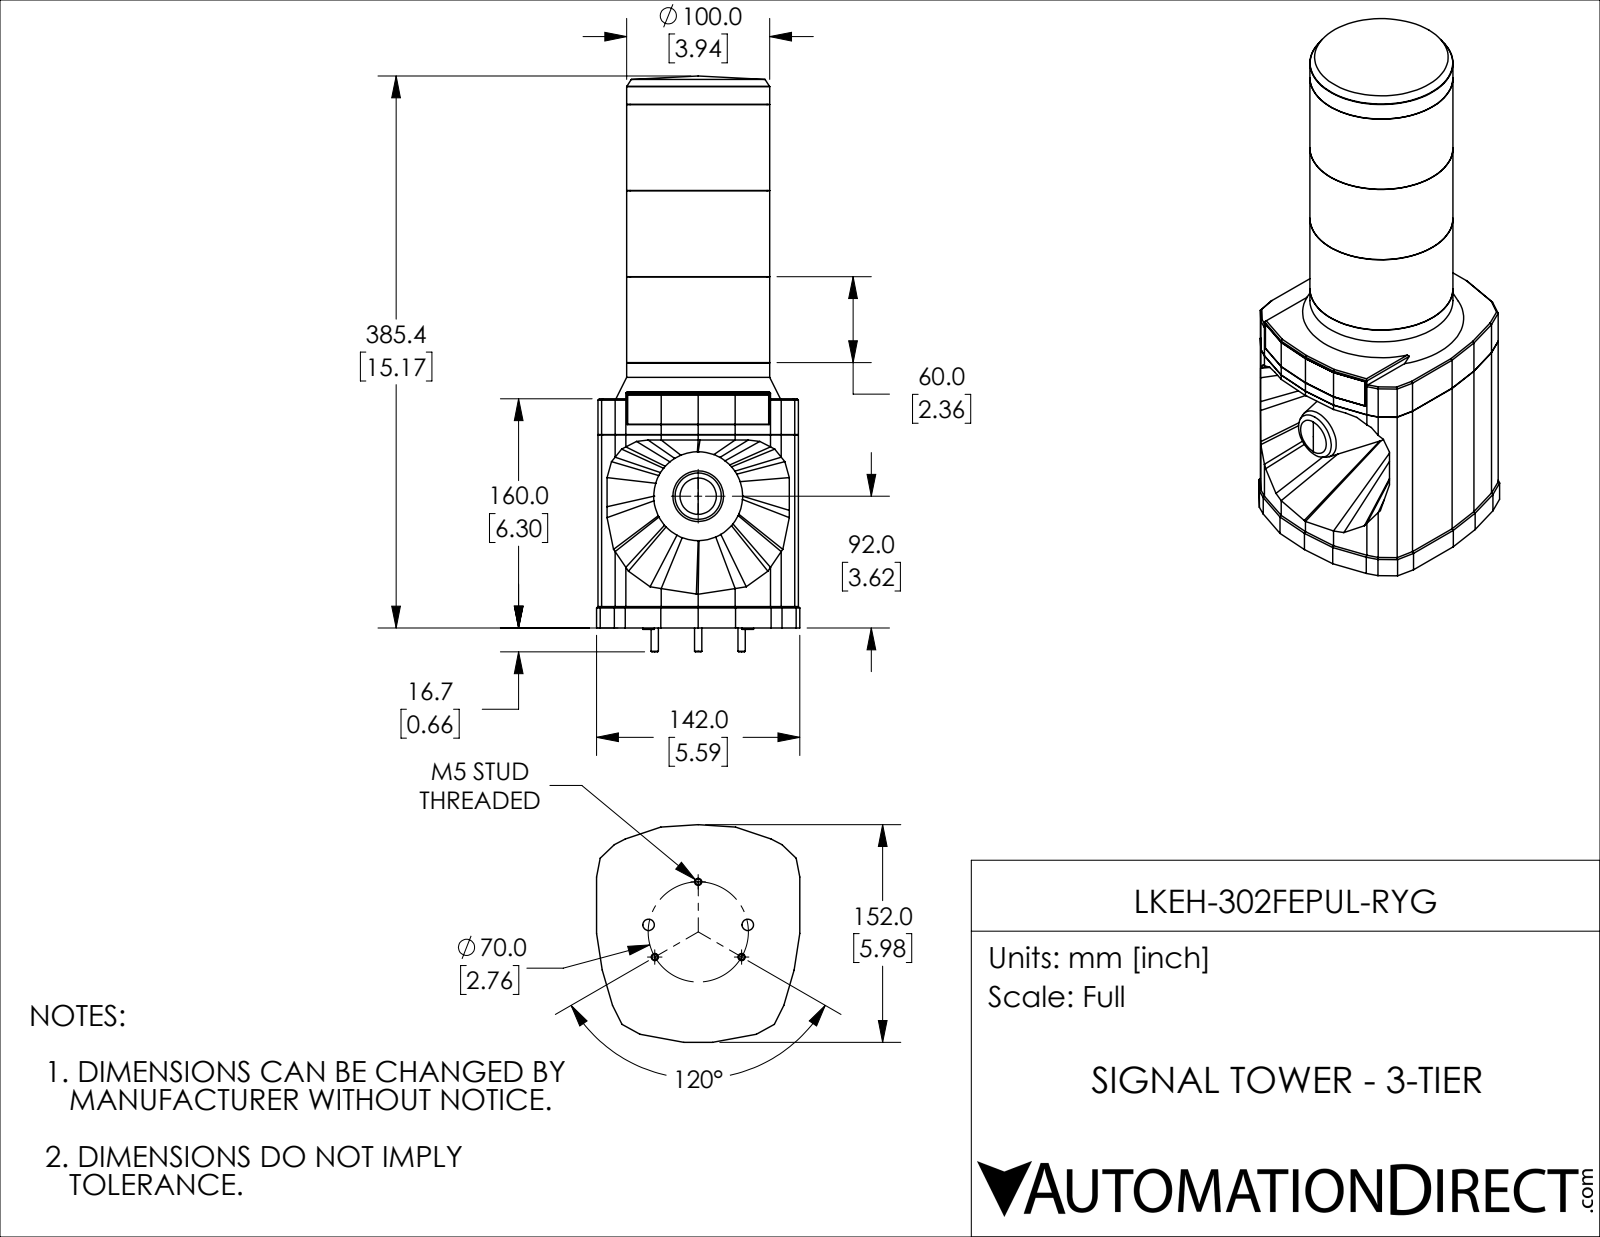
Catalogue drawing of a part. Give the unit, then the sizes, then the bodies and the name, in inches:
Units: inches
Overall size (bounding box): 15.831 × 5.984 × 5.591
Round bosses / shafts (diameter × count): ⌀0.197 ×3, ⌀0.315 ×2, ⌀3.937 ×1, ⌀3.764 ×1
Main face-to-face distances: 0.039, 5.512, 6.299, 2.366, 6.496, 0.197, 2.362, 2.37, 4.732, 4.728
Volume: 260.6 in³ · Surface area: 335.2 in²
Bodies: 1 solid, 274 faces (184 planar, 28 cylindrical, 62 other)
Part name (STEP PRODUCT): LKEH-302FEPUL-RYG
STEP written by: SolidWorks 2018 (AUTOMOTIVE_DESIGN)
